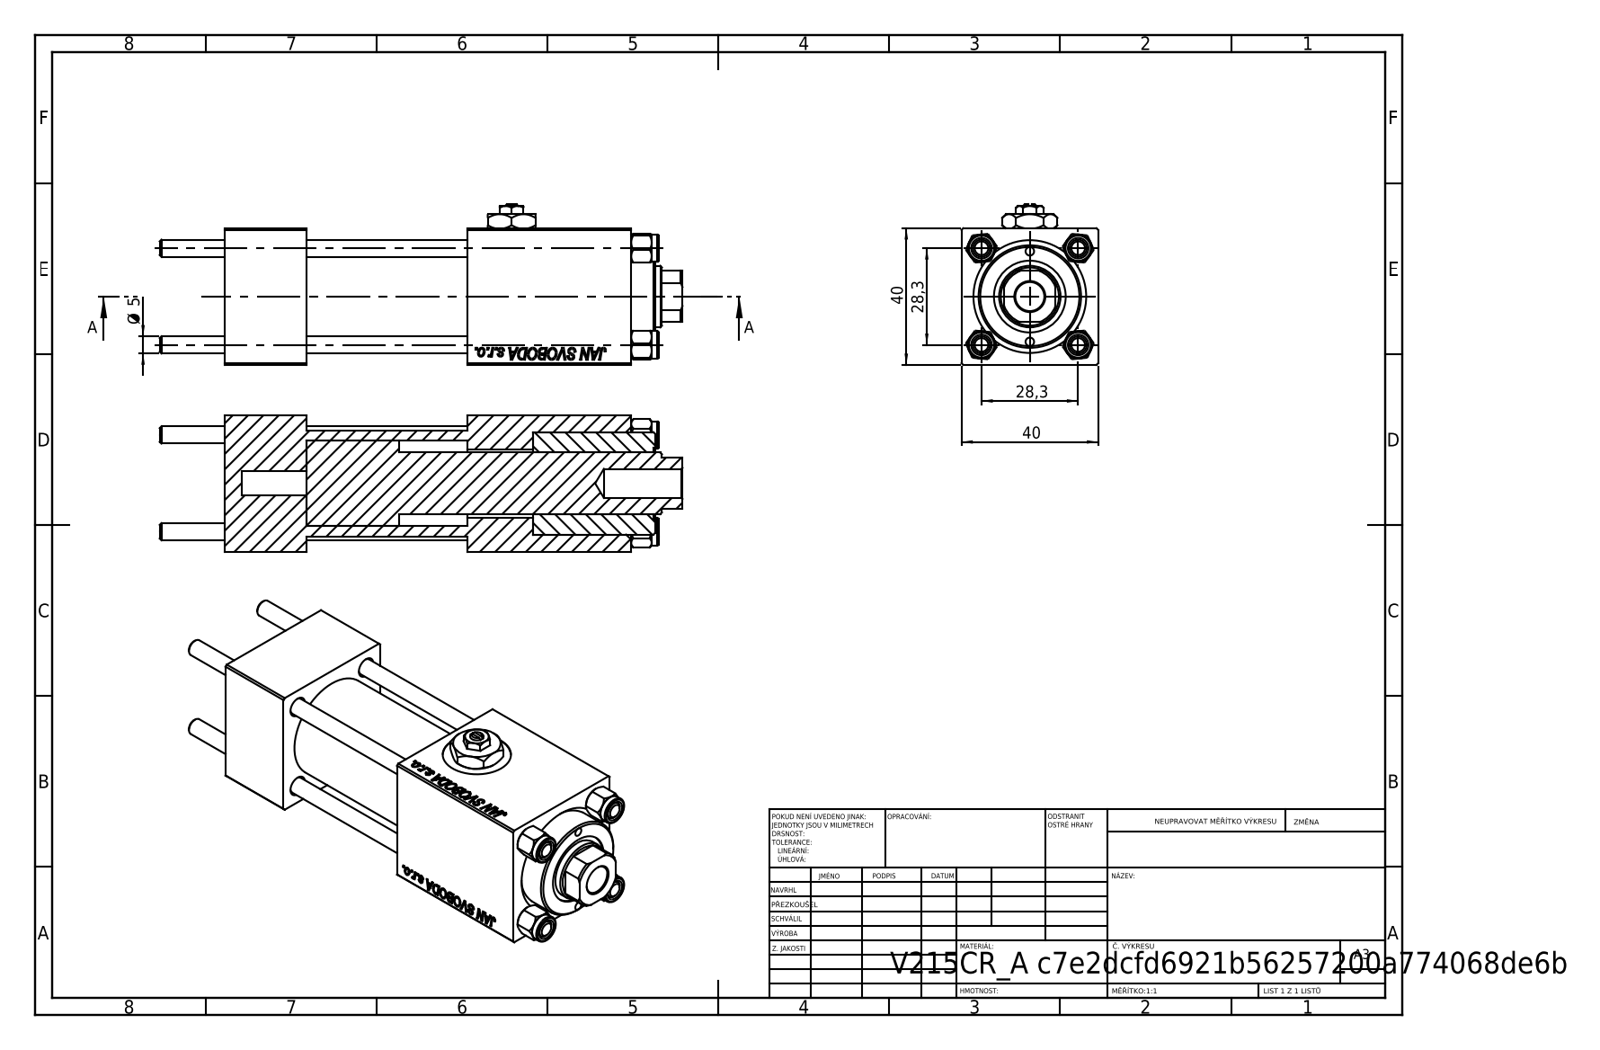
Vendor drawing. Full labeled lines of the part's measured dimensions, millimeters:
Part name (STEP PRODUCT): V215_VC_A; CR025_012_A_0_G_A_G_M_020_+#_##_TYCINKA; V215CR_VCP; V215CR_BODY_A (+2 more)
STEP written by: SolidWorks 2019 (CONFIG_CONTROL_DESIGN)
Units: millimetres
Bodies: 12 solids, 1182 faces (542 planar, 84 cylindrical, 556 other)
Overall size (bounding box): 153 × 47 × 40
Volume: 151 662 mm³ · Surface area: 62 079 mm²
Round holes (diameter × count): ⌀5 ×4, ⌀20 ×3, ⌀2.5 ×2, ⌀7 ×2, ⌀13.16 ×2, ⌀8.5 ×1, ⌀18 ×1, ⌀21 ×1, ⌀25 ×1, ⌀30 ×1
Round bosses / shafts (diameter × count): ⌀8 ×4, ⌀31 ×1
Partial cylindrical surfaces — rounded edges, fillets, slot ends (radius × count): R8.5 ×1
Main face-to-face distances: 40, 24, 47, 71, 90.3, 66.3, 19.3, 48, 119, 95
Hole centre spacings: 14.18, 20.01, 28.3, 30.84, 13.25, 40.02, 26.5, 72
